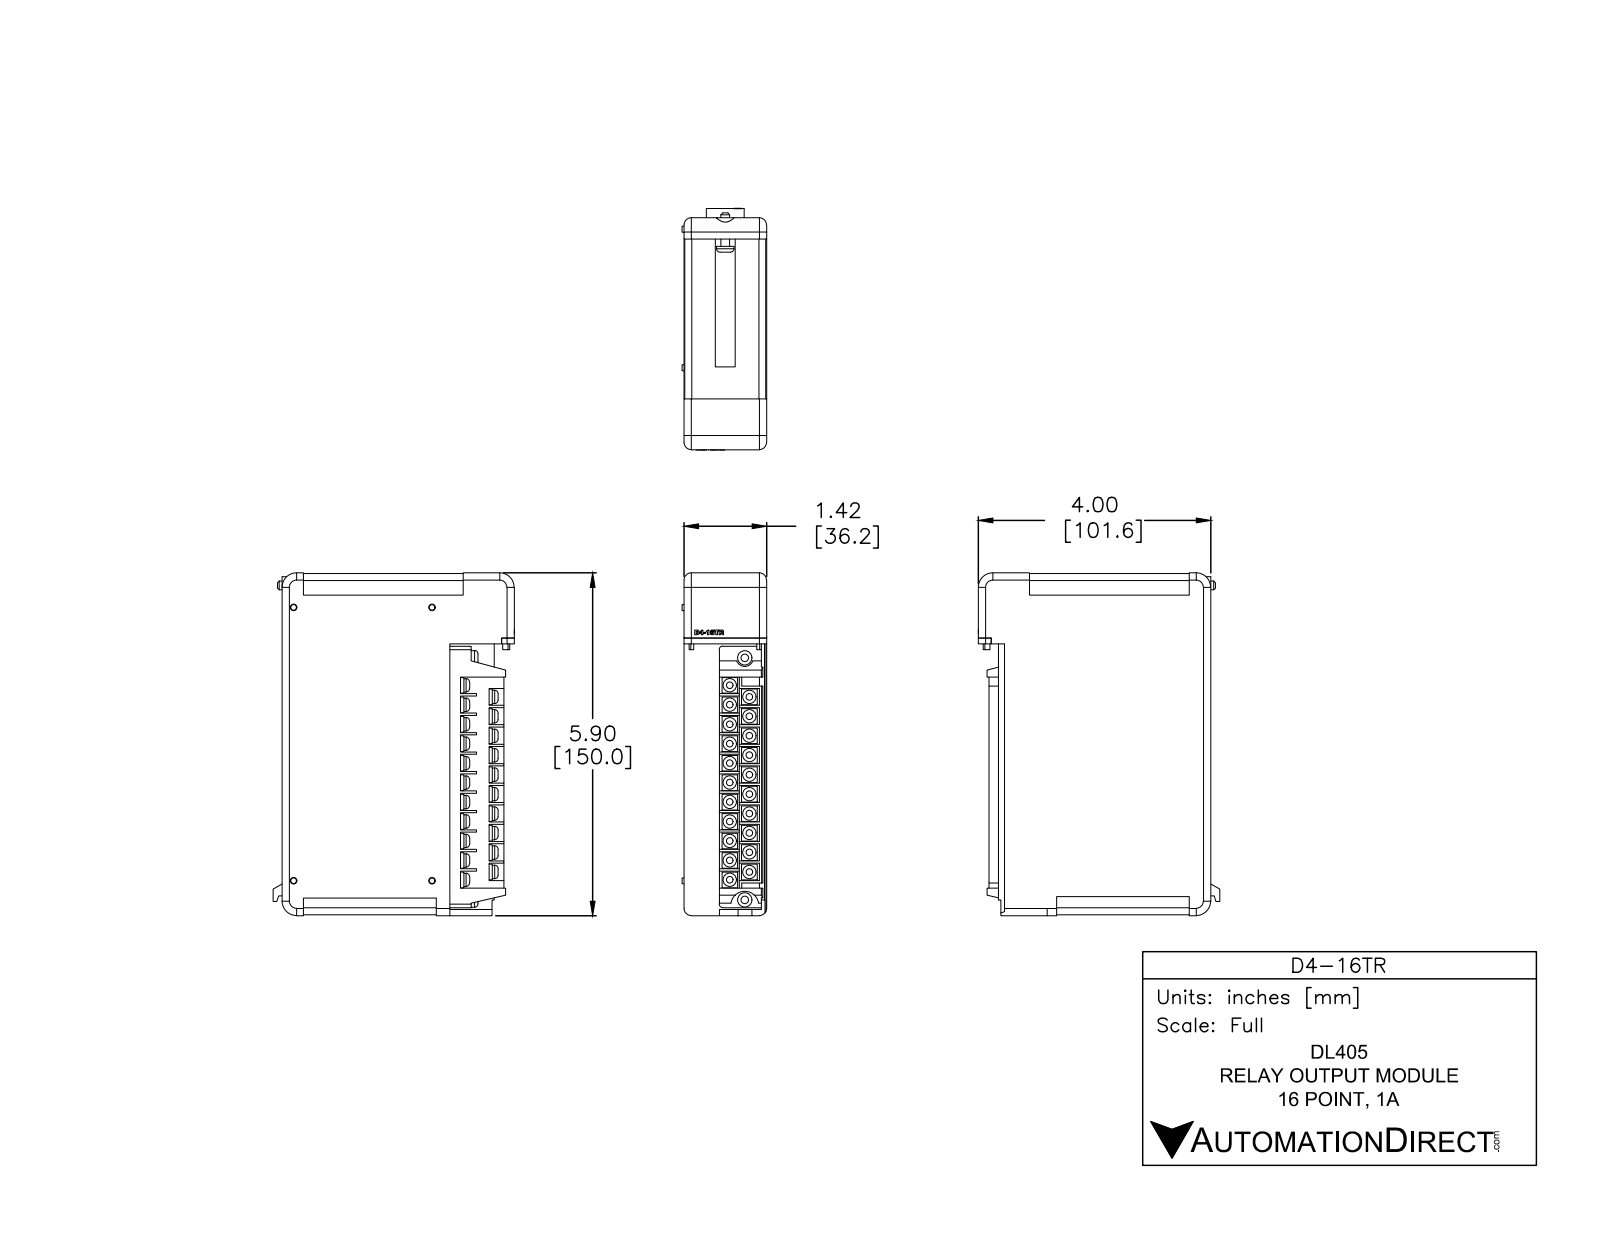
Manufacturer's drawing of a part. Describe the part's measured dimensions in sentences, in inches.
The part is named "D4-16TR". Its 3-D file was written by "SolidWorks 2014 (AUTOMOTIVE_DESIGN)". It is 6 solids with 886 faces: 548 planar, 246 cylindrical and 92 other. Overall it measures 5.905 by 4.223 by 1.455 inches. Its volume is 27.6 cubic inches and its surface area 90.48 square inches. Round bosses or shafts: 21 of diameter 0.23, 20 of diameter 0.035, 20 of diameter 0.035, 2 of diameter 0.25, 1 of diameter 0.3, 1 of diameter 0.15. Partial cylindrical surfaces (rounded edges, fillets, slot ends): 82 of radius 0.015, 8 of radius 0.125, 4 of radius 0.12, 3 of radius 0.25, 2 of radius 0.03, 2 of radius 0.06, 1 of radius 0.149, 1 of radius 0.151. The main face-to-face distances are 1.425, 0.015, 2.89, 5.875, 1.41, 0.47, 0.955, 5.89, 1.21, 0.345.
